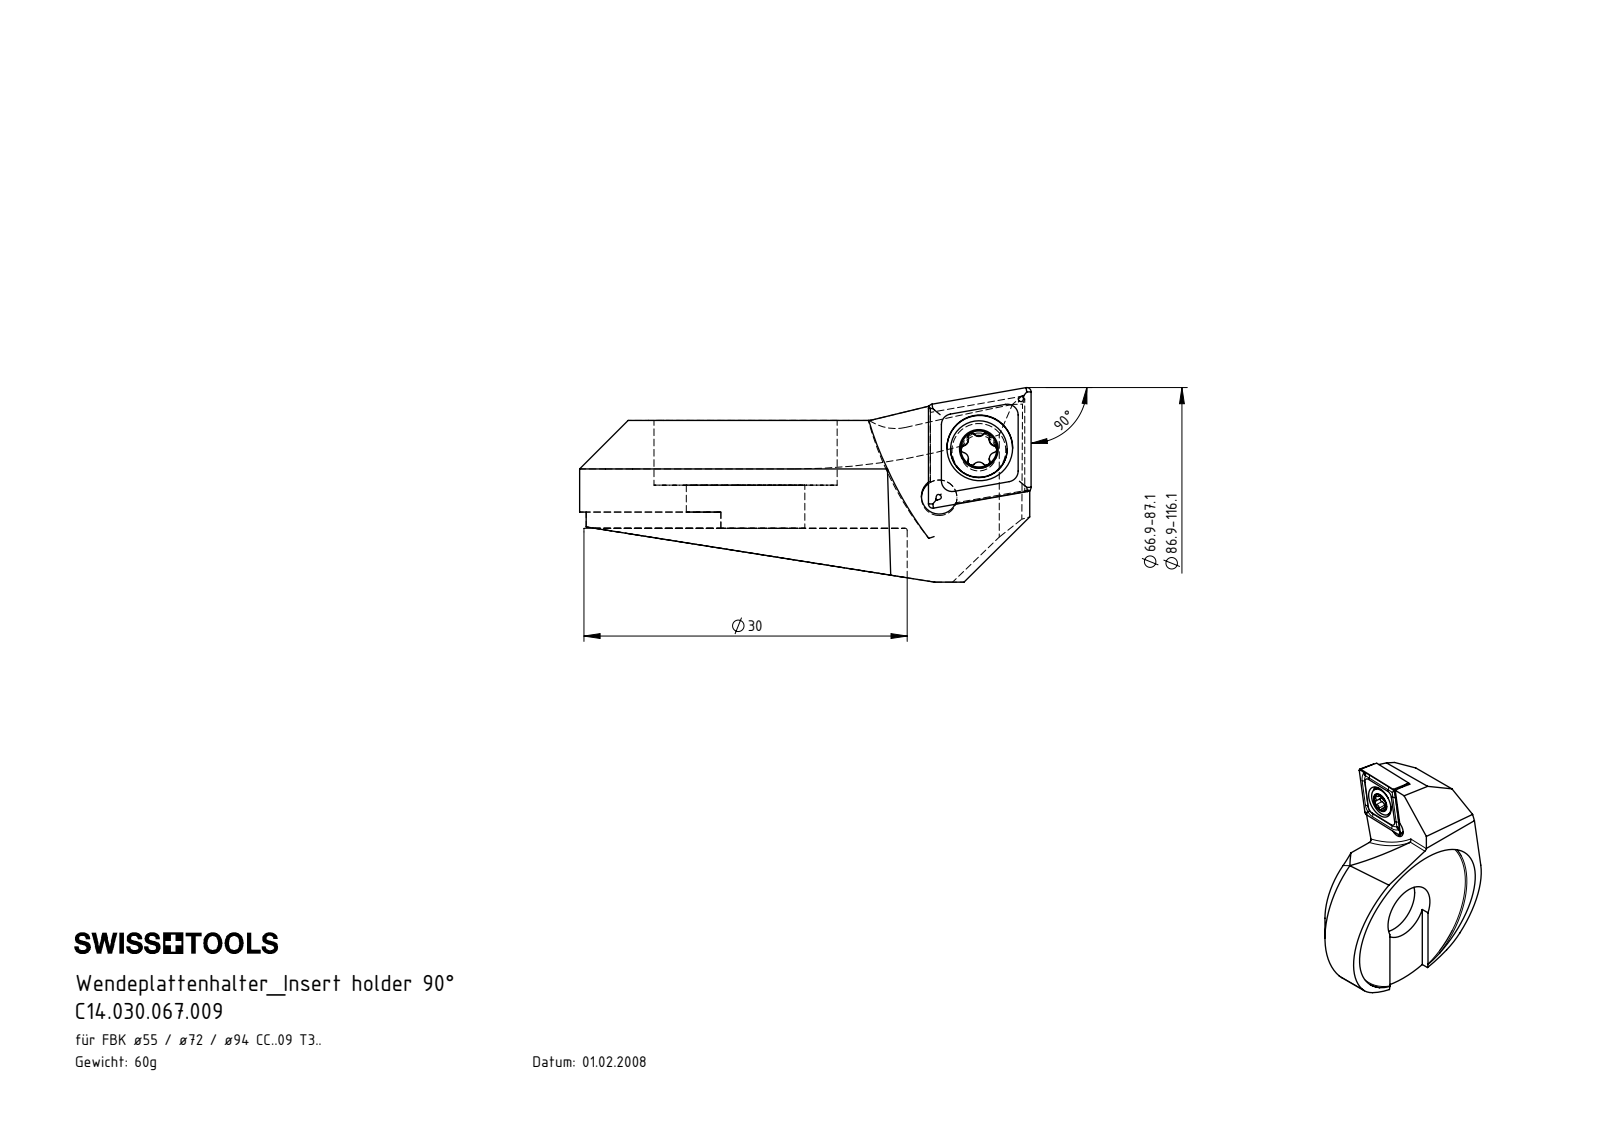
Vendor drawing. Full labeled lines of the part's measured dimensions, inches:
Part name (STEP PRODUCT): F55-WCA.001.013_D_fertigbearbeitet; CCMT060204; WCA-ER2.001.005_A; C14.030.067.009
STEP written by: SolidWorks 2017 (CONFIG_CONTROL_DESIGN)
Units: inches
Bodies: 5 solids, 153 faces (48 planar, 48 cylindrical, 57 other)
Overall size (bounding box): 1.65 × 1.303 × 0.711
Volume: 0.49 in³ · Surface area: 7.082 in²
Round holes (diameter × count): ⌀0.081 ×1, ⌀0.083 ×1, ⌀0.11 ×1, ⌀0.152 ×1, ⌀0.433 ×1, ⌀0.669 ×1, ⌀1.181 ×1
Round bosses / shafts (diameter × count): ⌀0.134 ×1, ⌀0.098 ×1
Partial cylindrical surfaces — rounded edges, fillets, slot ends (radius × count): R0.008 ×6, R0.014 ×5, R0.02 ×2, R0.394 ×2, R0.014 ×1, R0.041 ×1, R0.197 ×1, R0.652 ×1
Main face-to-face distances: 0.394, 0.354, 0.039, 0.197, 0.236, 0.157, 0.335, 0.295, 0.098, 0.059
Hole centre spacings: 0.154, 0.159
